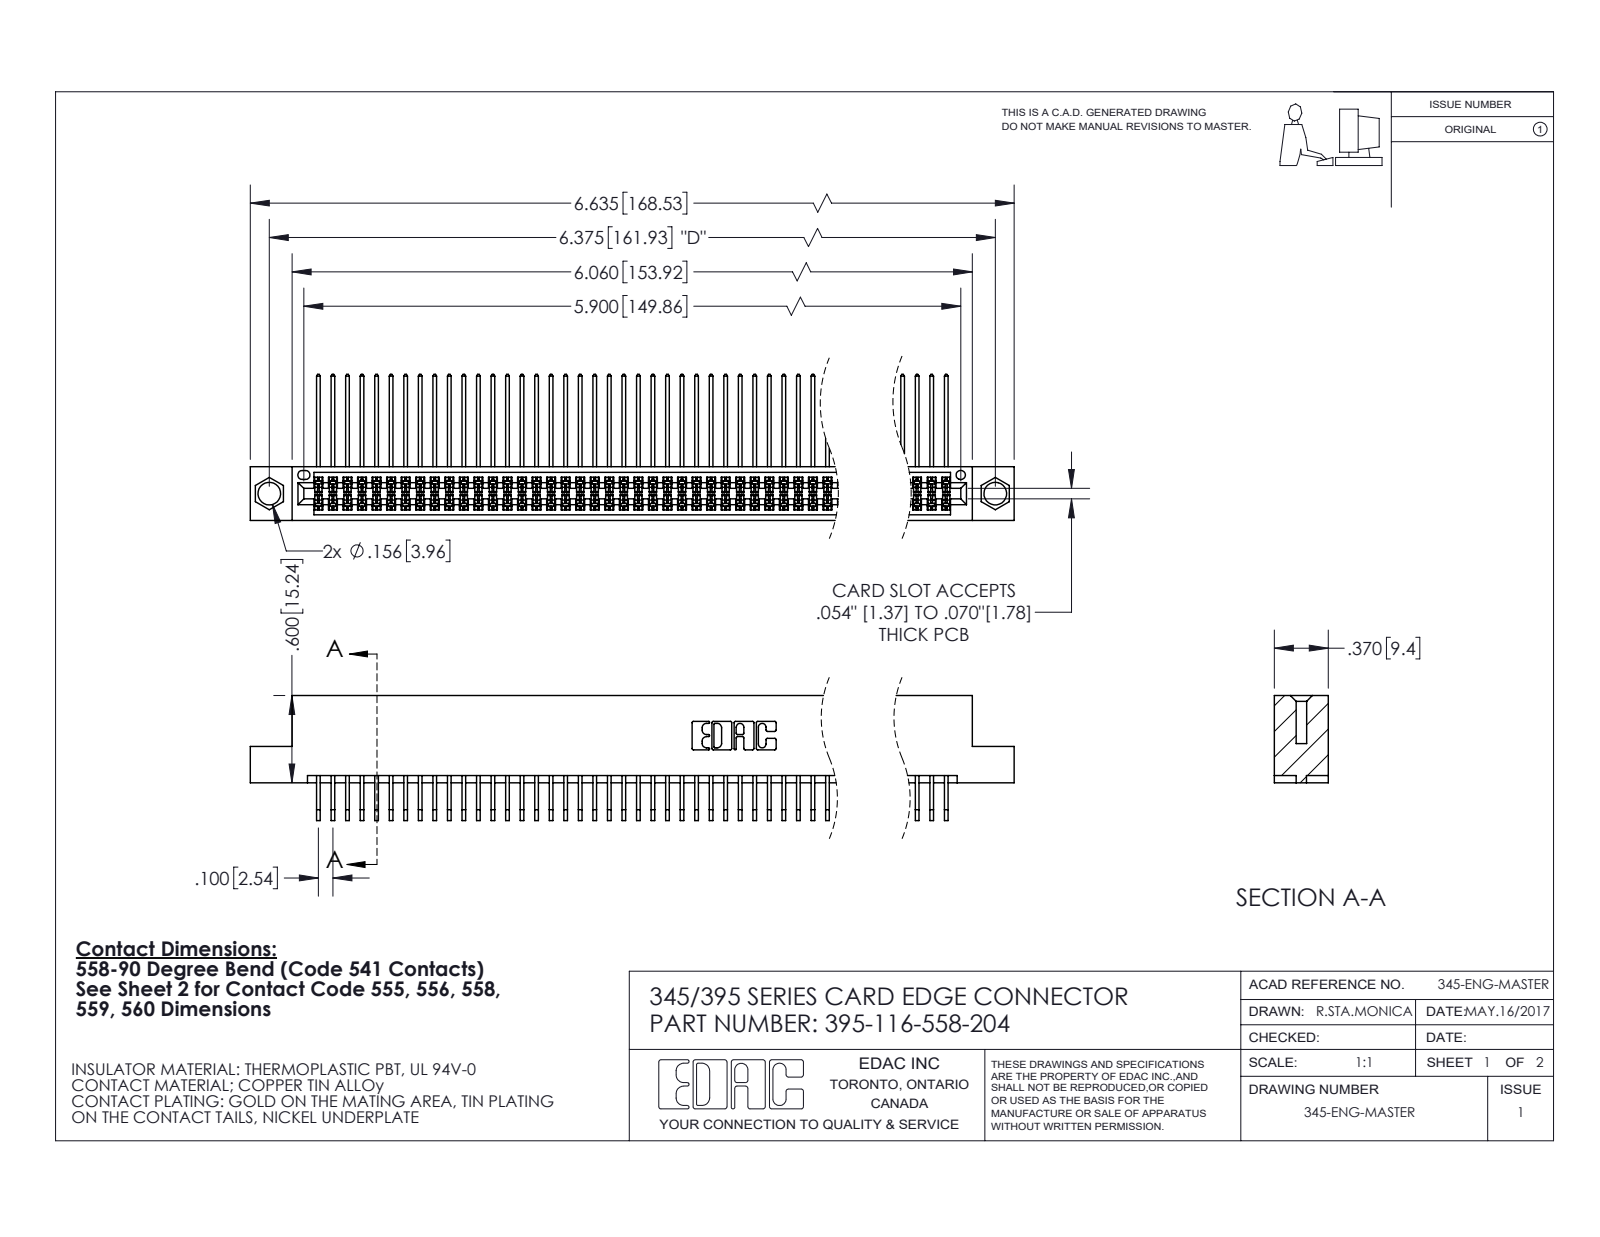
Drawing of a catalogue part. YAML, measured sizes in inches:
part_name: "395-116-558-204; 345-292-001_558 Tail - 2; 345 Part_Flush Mounting Lugs - 0.156 Dia-TI; 345-292-001_558 559 Tail - 1"
step_written_by: "SolidWorks 2020 (CONFIG_CONTROL_DESIGN)"
units: inches
bodies: {solids: 117, faces: 6172, planar: 4154, cylindrical: 2018, other: 0}
overall_size: [6.635, 1.005, 0.859]
volume: 1.042
surface_area: 44.27
round_holes:
  - {diameter: 0.156, count: 2}
  - {diameter: 0.064, count: 1}
partial_cylinders:
  - {radius: 0.006, count: 174}
  - {radius: 0.01, count: 22}
  - {radius: 0.007, count: 6}
  - {radius: 0.031, count: 6}
  - {radius: 0.026, count: 3}
  - {radius: 0.014, count: 2}
  - {radius: 0.019, count: 2}
  - {radius: 0.022, count: 2}
face_to_face_distances: [0.072, 0.298, 0.2, 0.37, 0.098, 0.272, 0.025, 0.225, 0.025, 0.175]
hole_center_spacings: [0.27, 6.139, 6.375]
